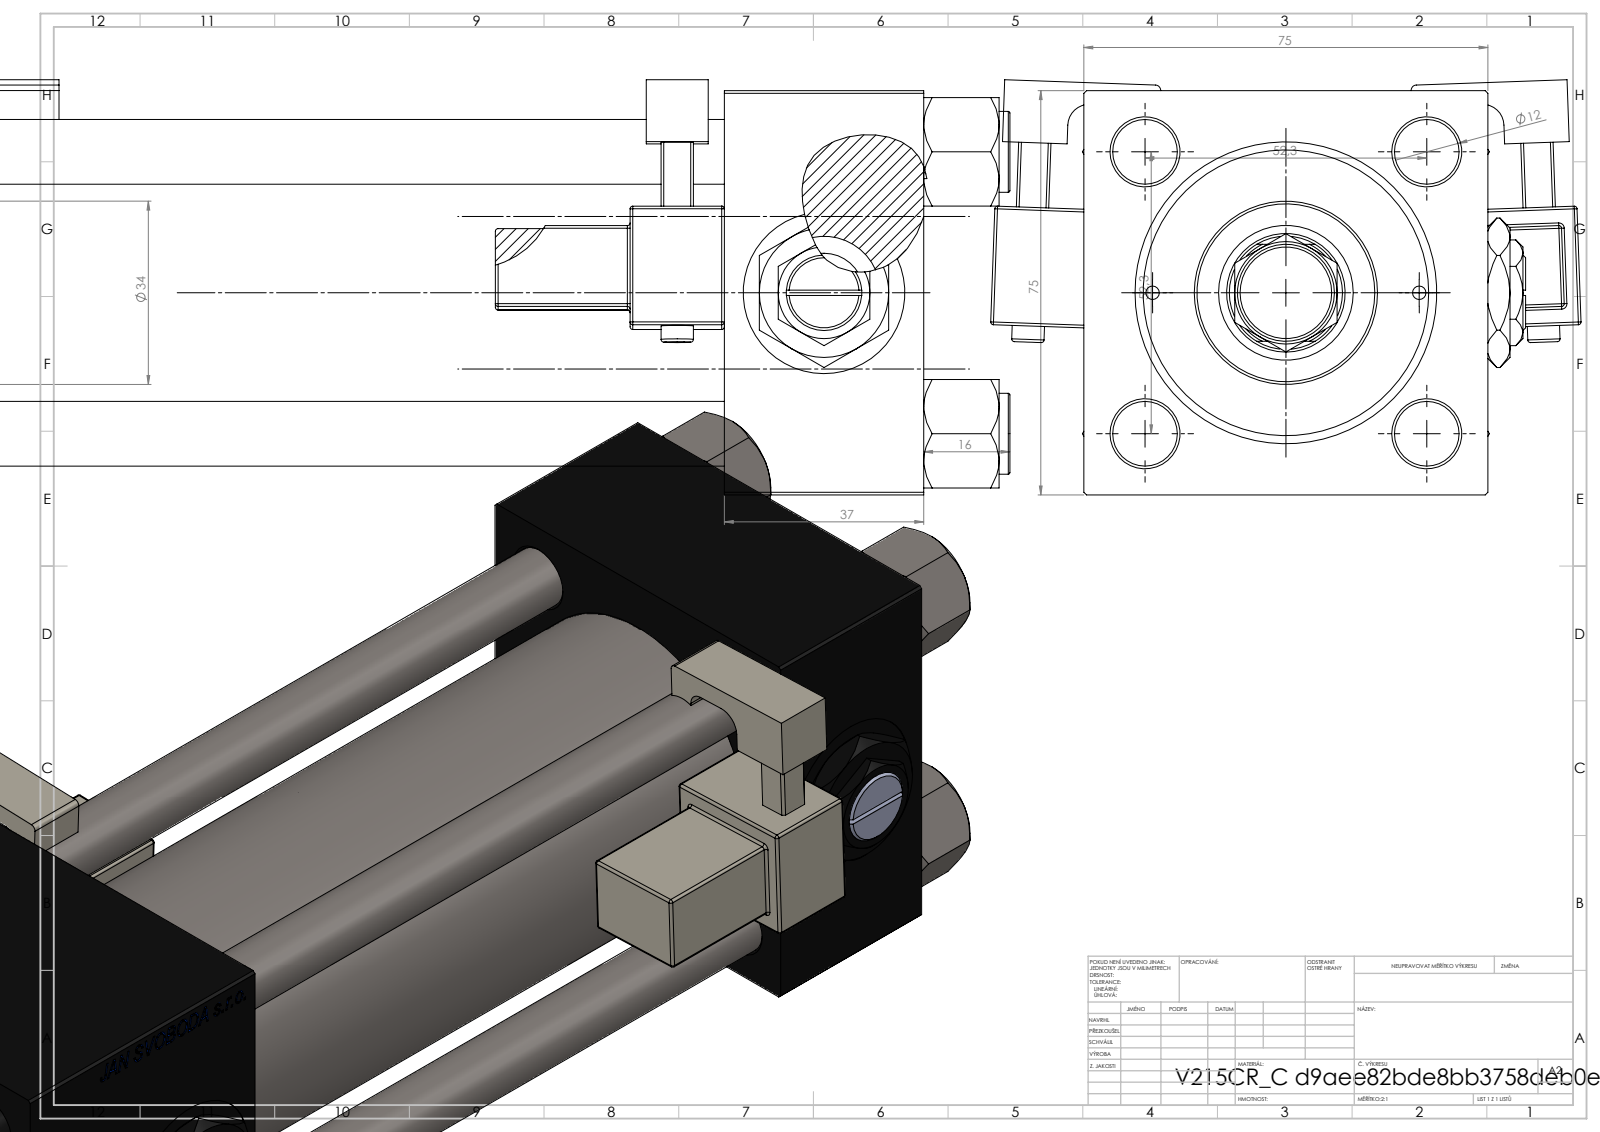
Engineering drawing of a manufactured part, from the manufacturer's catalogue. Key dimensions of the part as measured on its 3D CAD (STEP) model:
Part name (STEP PRODUCT): V215CR_VCP_C; V215CR_C_TYCINKA; MFA; Zatka_pro_OIL_PORT (+4 more)
STEP written by: SolidWorks 2019 (CONFIG_CONTROL_DESIGN)
Units: millimetres
Bodies: 16 solids, 1461 faces (649 planar, 166 cylindrical, 646 other)
Overall size (bounding box): 308 × 109.57 × 77.03
Volume: 807 566 mm³ · Surface area: 211 041 mm²
Round holes (diameter × count): ⌀12 ×4, ⌀2.5 ×2, ⌀7 ×2, ⌀20.96 ×2, ⌀30 ×2, ⌀10.5 ×1, ⌀22 ×1, ⌀25 ×1, ⌀41 ×1, ⌀50 ×1, ⌀53 ×1
Round bosses / shafts (diameter × count): ⌀15 ×4, ⌀6 ×2, ⌀56 ×1, ⌀34 ×1, ⌀18 ×1, ⌀11 ×1
Partial cylindrical surfaces — rounded edges, fillets, slot ends (radius × count): R0.5 ×48, R1 ×2, R2.5 ×2, R4 ×2, R10.5 ×1
Main face-to-face distances: 75, 37, 234, 197, 175, 138, 59, 205.3, 168.3, 30.3
Hole centre spacings: 26.19, 36.98, 52.3, 57.22, 24.75, 73.96, 49.5, 173.5
